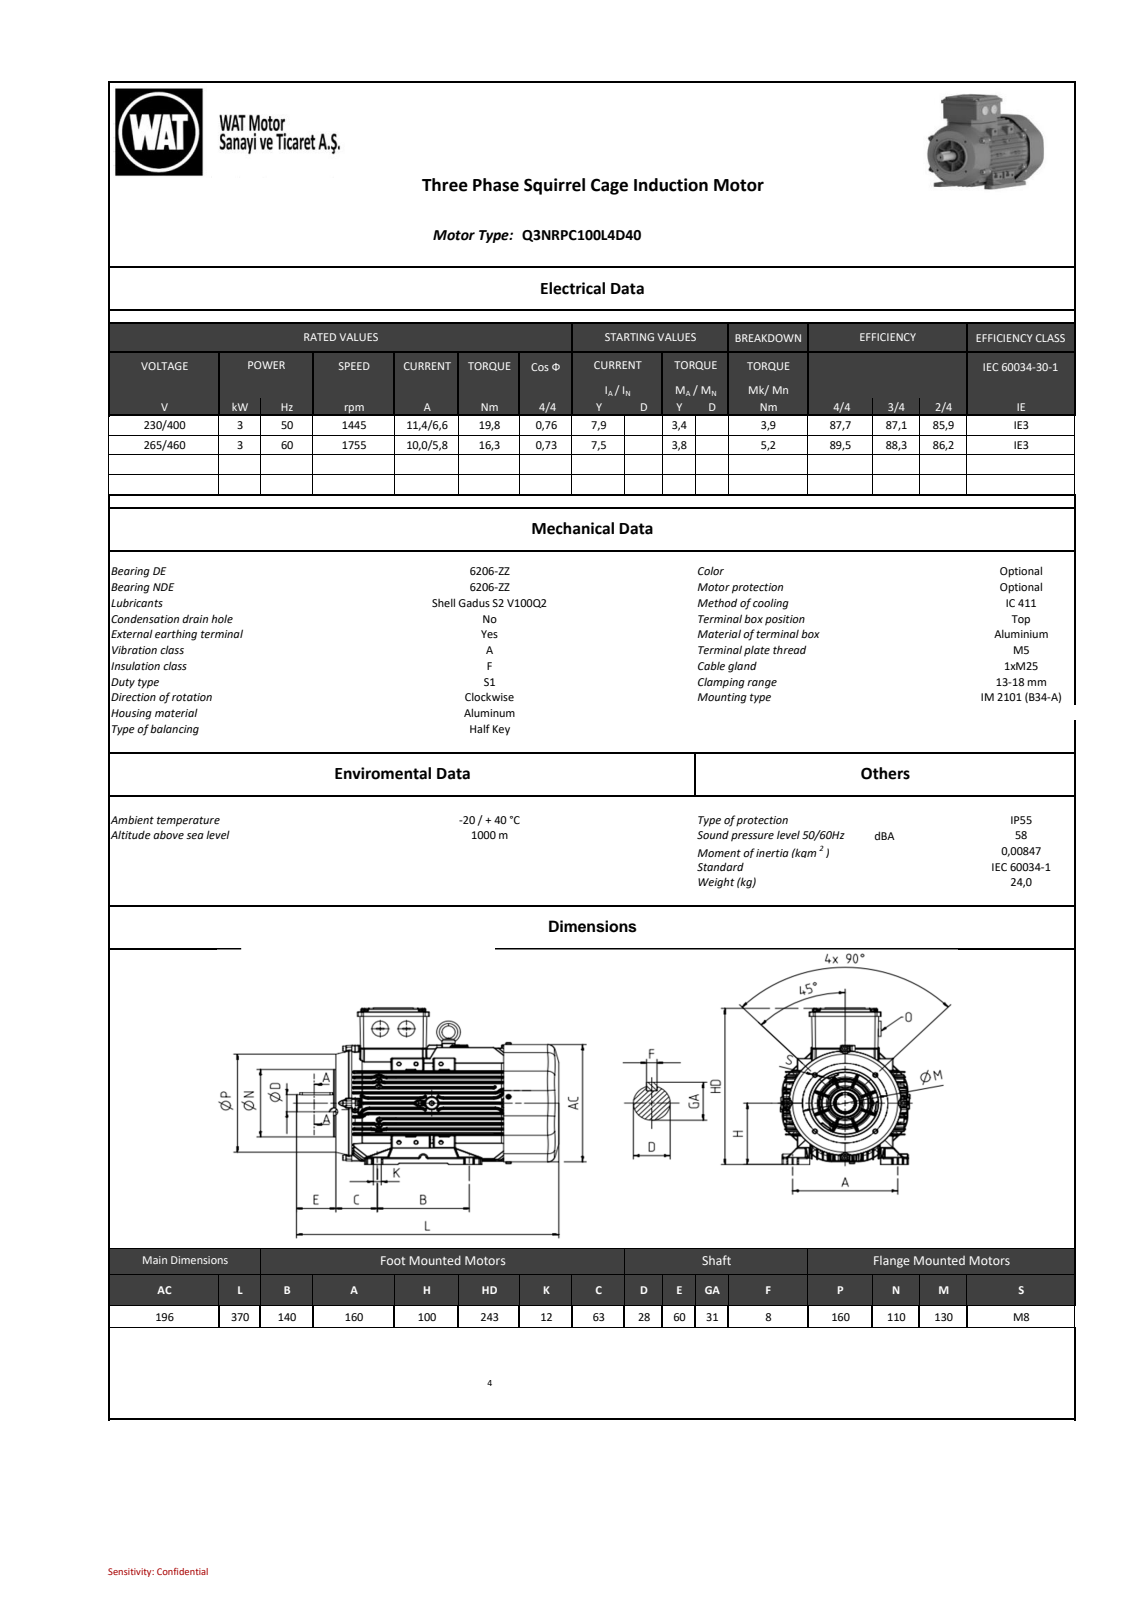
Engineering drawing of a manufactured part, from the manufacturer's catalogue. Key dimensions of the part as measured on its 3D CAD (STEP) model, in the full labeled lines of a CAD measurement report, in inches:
Part name (STEP PRODUCT): C90127E0127Fj83y
STEP written by: SIEMENS PLM Software NX 11.0 (AUTOMOTIVE_DESIGN)
Units: inches
Bodies: 0 solids, 14485 faces (2923 planar, 4378 cylindrical, 7184 other)
Overall size (bounding box): 14.567 × 9.075 × 7.874
Round holes (diameter × count): ⌀0.197 ×6, ⌀0.256 ×6, ⌀0.079 ×2, ⌀0.098 ×2, ⌀0.118 ×2, ⌀0.472 ×2, ⌀0.984 ×2, ⌀0.157 ×1, ⌀0.335 ×1, ⌀0.413 ×1, ⌀1.126 ×1, ⌀1.297 ×1
Round bosses / shafts (diameter × count): ⌀0.315 ×7, ⌀0.157 ×7, ⌀0.465 ×6, ⌀0.394 ×6, ⌀0.236 ×6, ⌀1.378 ×2, ⌀1.094 ×2, ⌀0.994 ×2
Partial cylindrical surfaces — rounded edges, fillets, slot ends (radius × count): R0.02 ×1252, R0.03 ×576, R0.031 ×526, R0.039 ×321, R0.01 ×144, R0.157 ×100, R0.079 ×77, R0.059 ×70
Main face-to-face distances: 0.031, 0.079, 0.551, 0.208, 0.118, 1.102, 1.614, 11.772, 1.583, 11.74
Hole centre spacings: 3.622, 1.535, 3.785, 6.177, 7.244, 0.478, 0.556, 0.672
